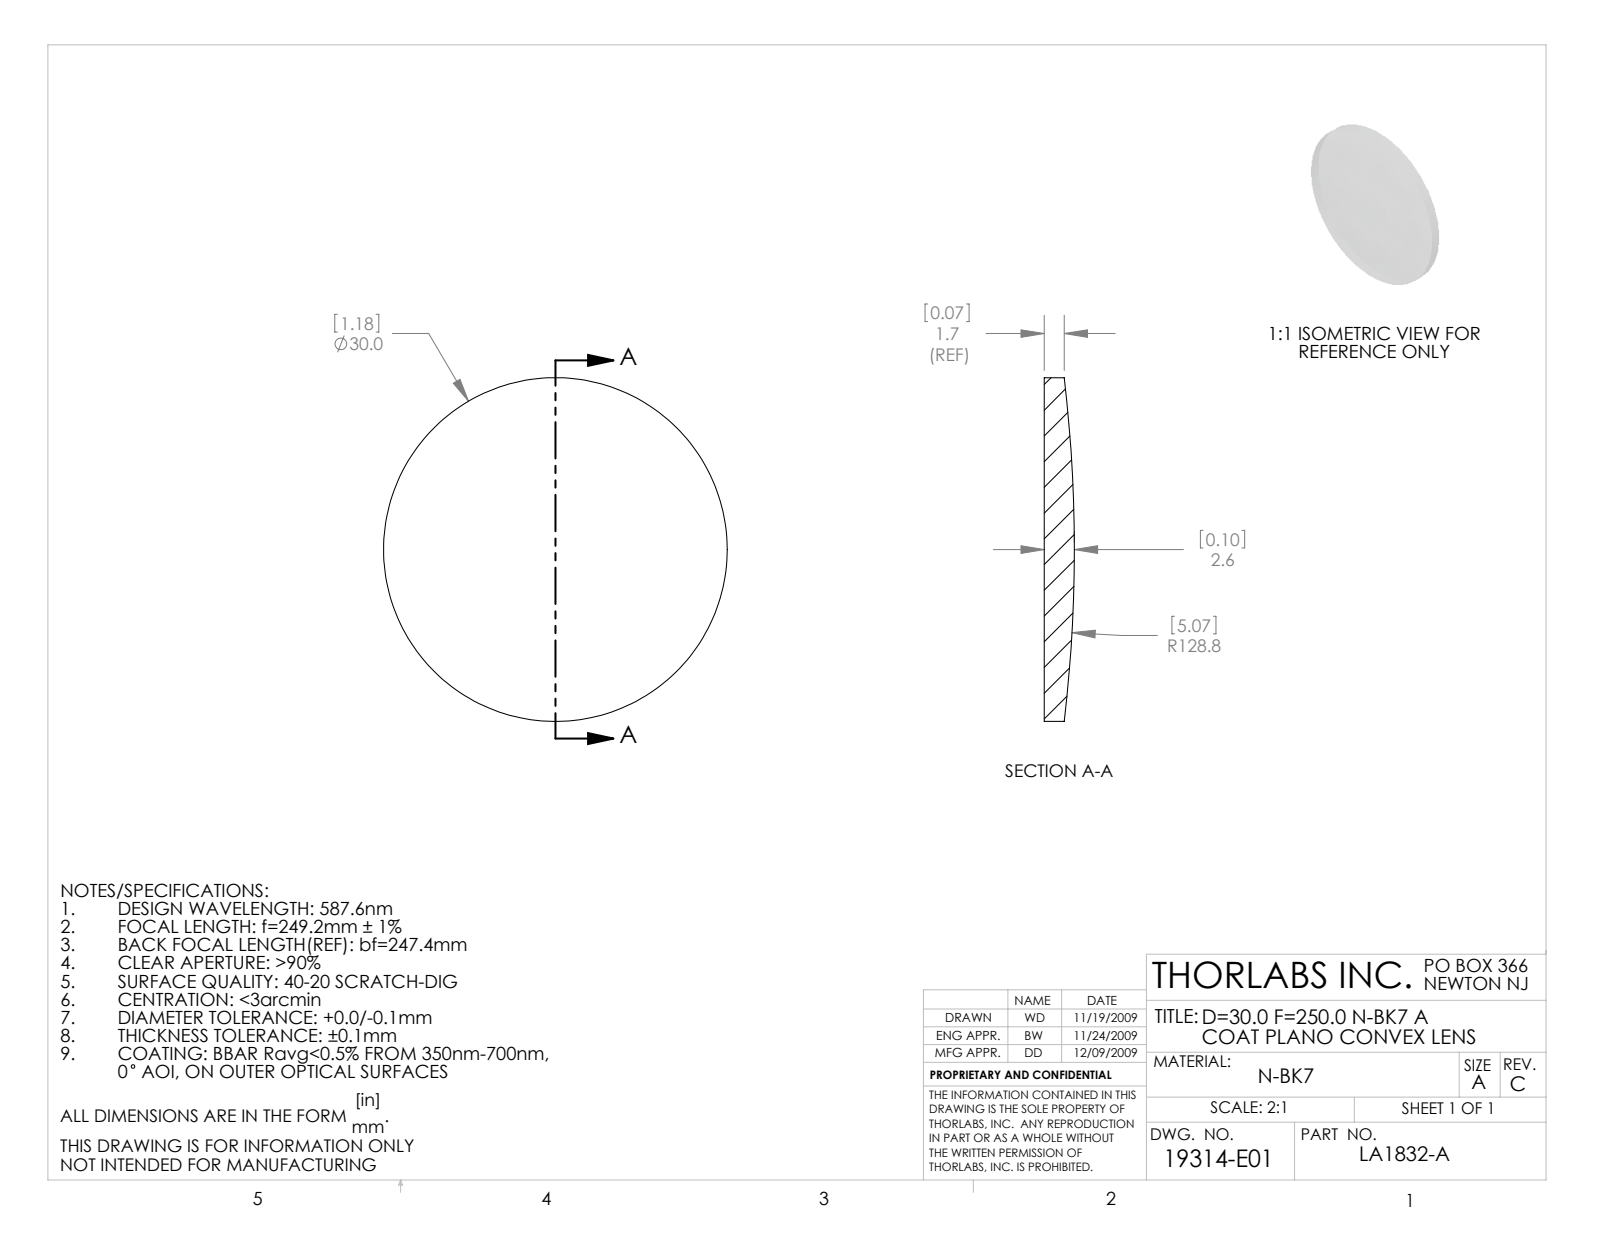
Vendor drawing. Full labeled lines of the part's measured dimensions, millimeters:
Part name (STEP PRODUCT): 19314-E0W
STEP written by: SolidWorks 2009 (AUTOMOTIVE_DESIGN)
Units: millimetres
Bodies: 1 solid, 5 faces (1 planar, 2 cylindrical, 2 other)
Overall size (bounding box): 30 × 30 × 2.62
Volume: 1 542 mm³ · Surface area: 1 580 mm²
Round bosses / shafts (diameter × count): ⌀30 ×1
